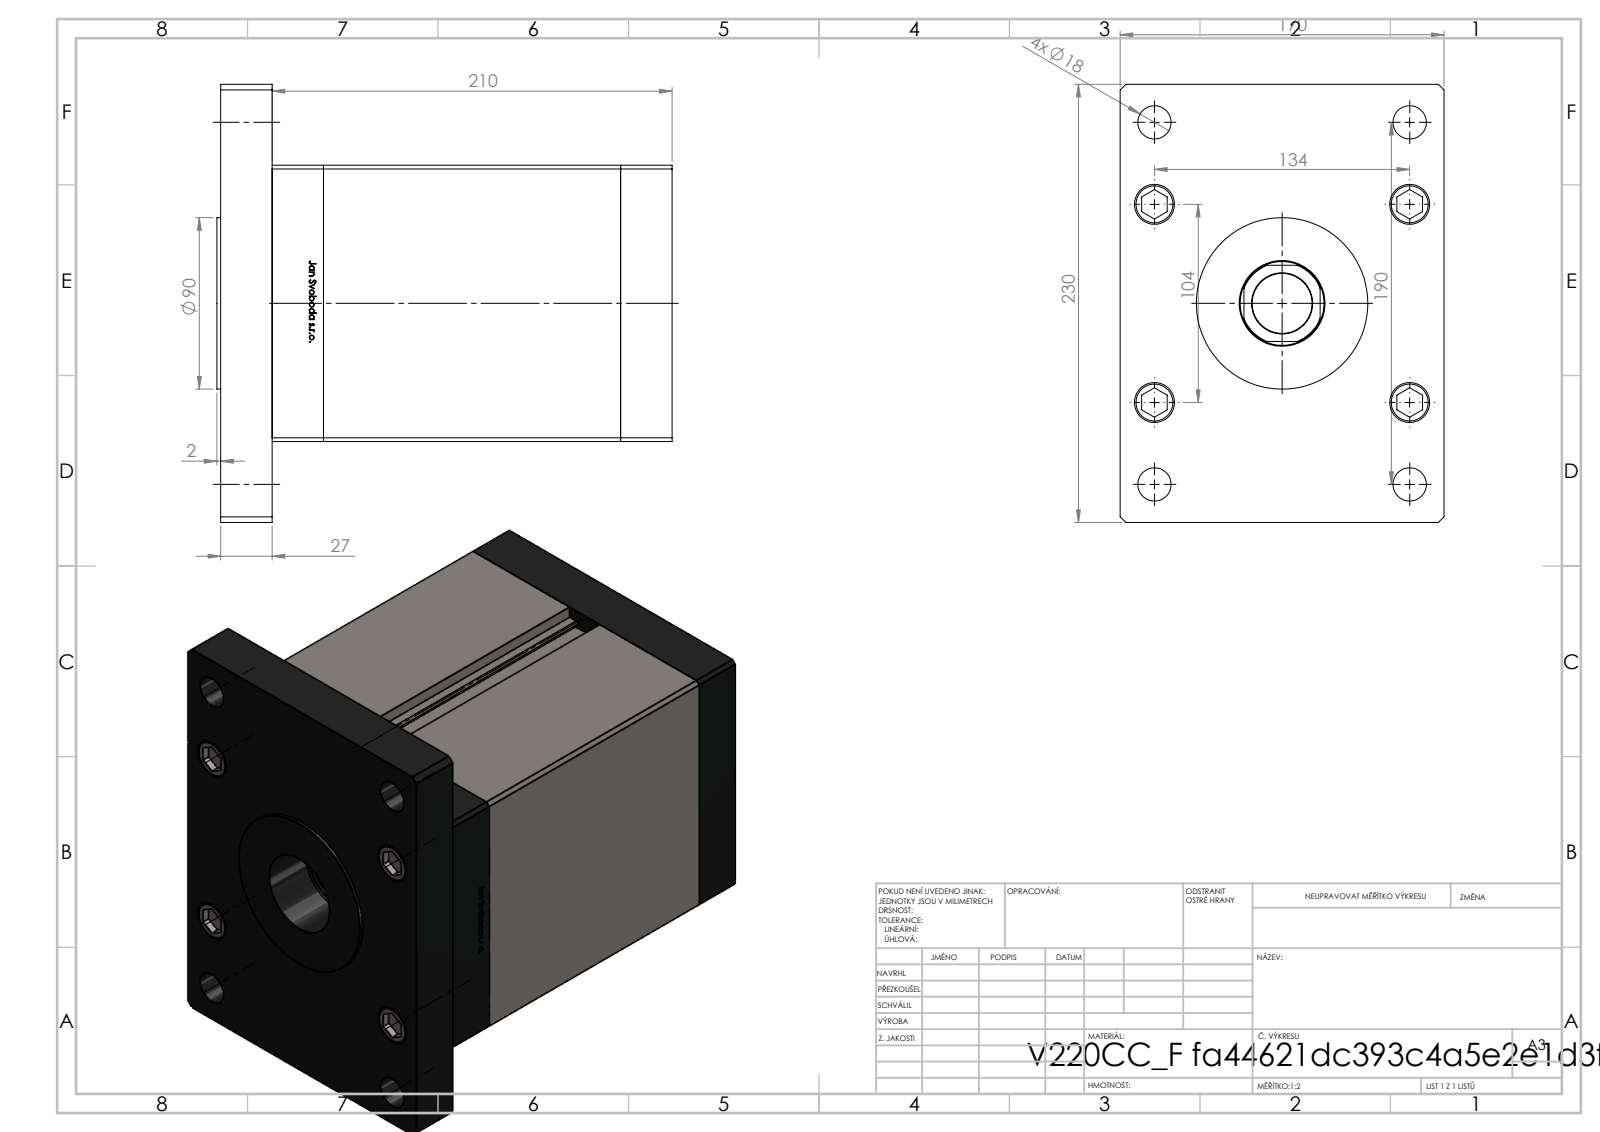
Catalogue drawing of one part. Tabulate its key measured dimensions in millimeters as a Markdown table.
| quantity | value |
| --- | --- |
| part name | ALLEN BOLT; V220C BACK_F; V220C_F_MIDDLE; V220C_F (+2 more) |
| STEP written by | SolidWorks 2019 (CONFIG_CONTROL_DESIGN) |
| units | millimeters |
| bodies | 19 solids, 1310 faces (517 planar, 187 cylindrical, 606 other) |
| overall size | 239 × 230 × 170 |
| volume | 5 300 000 mm³ |
| surface area | 542 506 mm² |
| round holes (diameter × count) | 17.5 × 9, 22 × 5, 16 × 4, 21 × 4, 2 × 2, 13.16 × 2, 31.5 × 1, 45 × 1, 46.5 × 1 |
| round bosses / shafts (diameter × count) | 8 × 9, 21 × 5, 100 × 1, 90 × 1 |
| partial cylindrical surfaces (radius × count) | 0.93 × 2, 22 × 1 |
| main face-to-face distances | 27, 183, 210, 170, 145, 156, 54, 237, 34.8, 7.8 |
| hole center spacings | 61, 43, 84.81, 116.25, 134, 140.73, 147, 198.91 |
